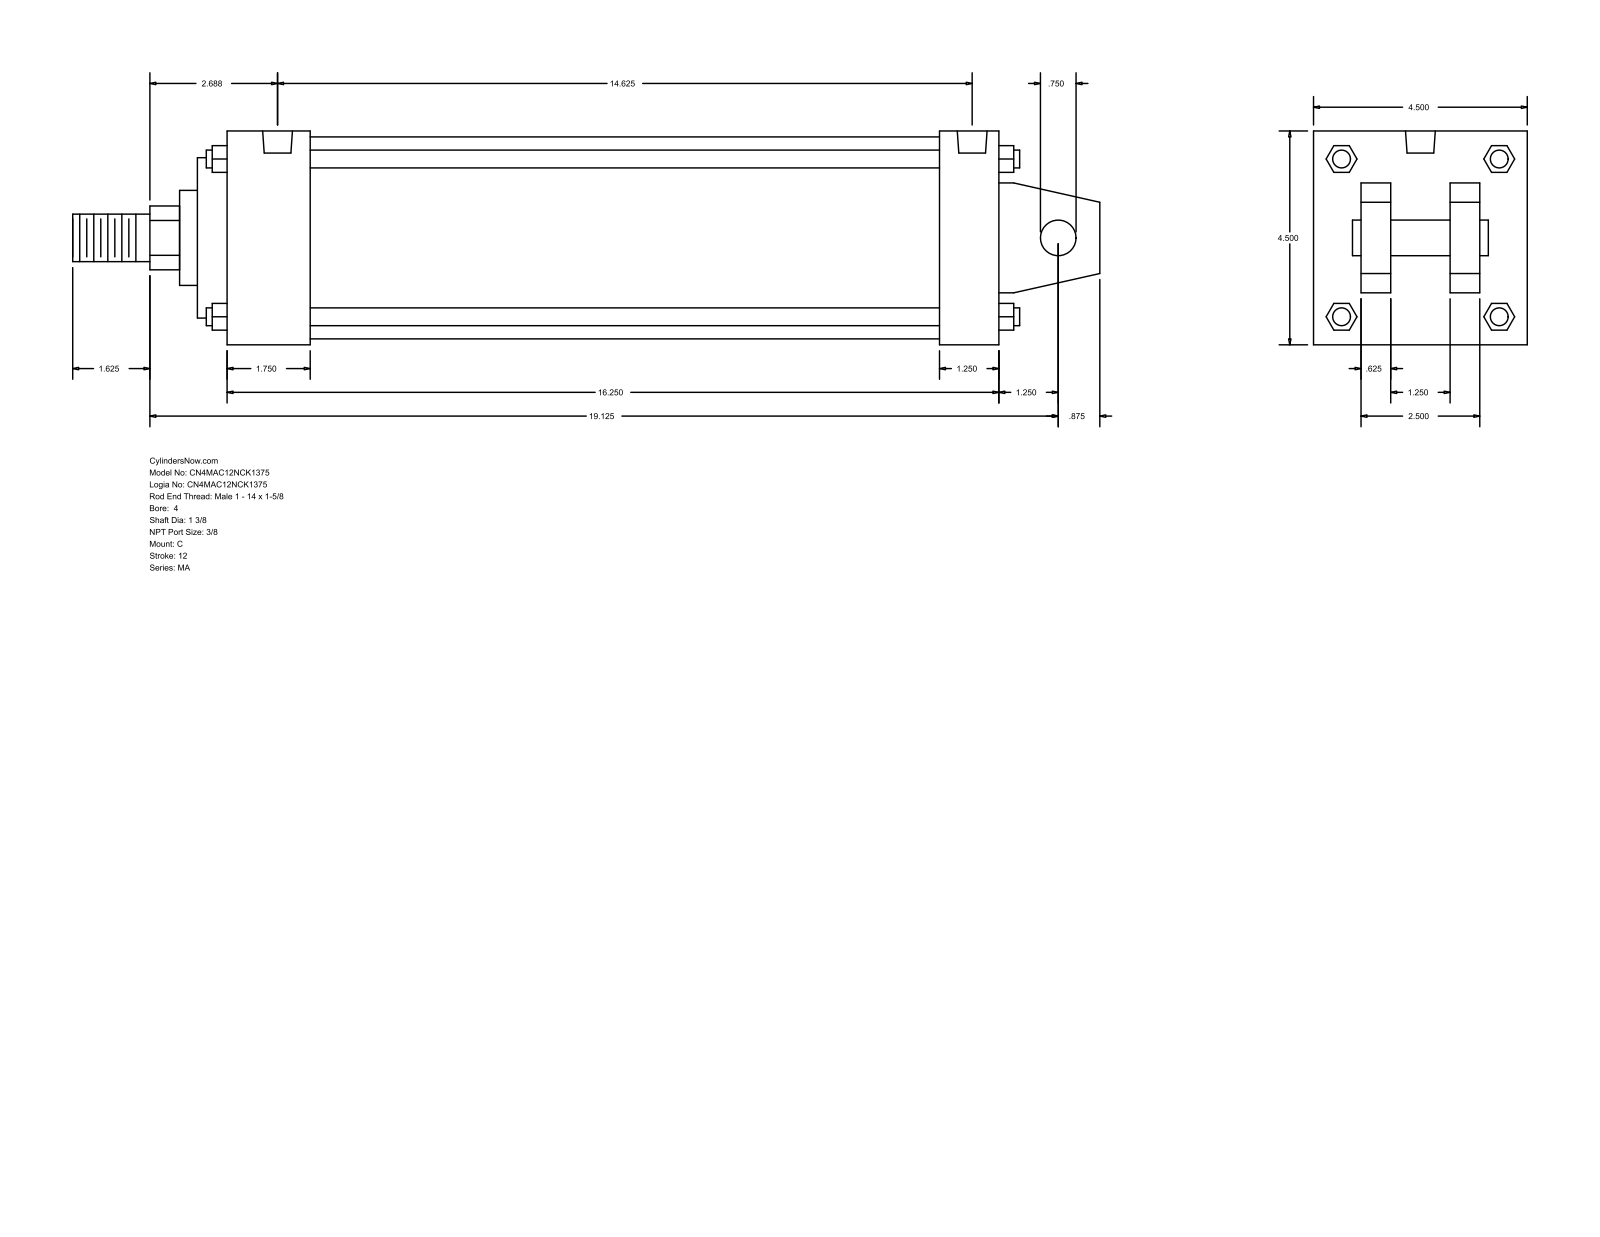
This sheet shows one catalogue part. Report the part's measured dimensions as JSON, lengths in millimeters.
{"part_name": "MA_C__0400_1.375", "step_written_by": "GSSL Pune (CONFIG_CONTROL_DESIGN)", "units": "millimeters", "bodies": {"solids": 0, "faces": 141, "planar": 109, "cylindrical": 32, "other": 0}, "overall_size": [549.27, 114.3, 114.3], "round_holes": [[11.11, 4], [15.93, 2]], "round_bosses_or_shafts": [[9.53, 4], [107.95, 1], [85.72, 1], [50.8, 1], [34.92, 1], [25.4, 1], [19.05, 1]], "partial_cylinders_radius": [[17.06, 1]], "face_to_face_distances": [114.3, 15.87, 412.75, 73.03, 41.27, 25.4, 88.9, 47.63, 428.62, 396.87], "hole_center_spacings": [361.95, 4.76, 4.77, 366.71, 366.72, 371.48]}
